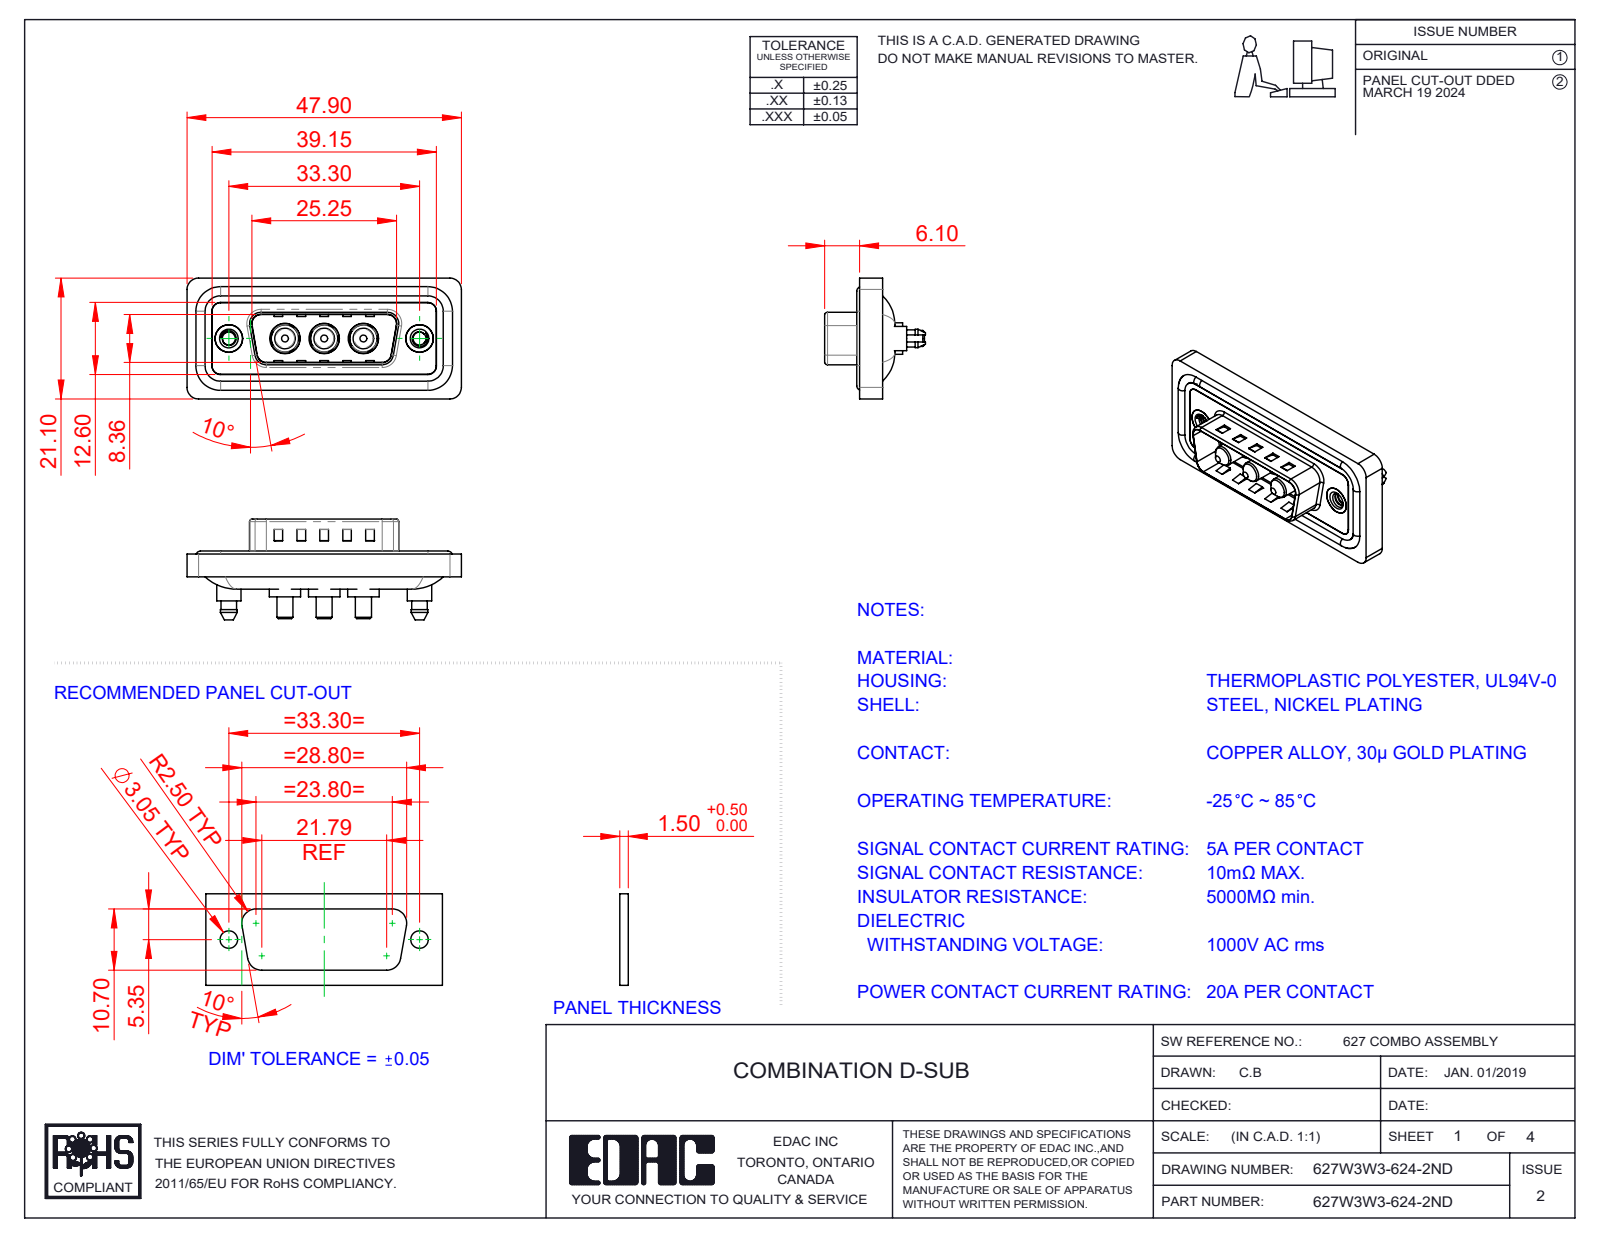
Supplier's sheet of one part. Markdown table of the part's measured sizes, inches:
| quantity | value |
| --- | --- |
| part name | 627Combo Waterproof Housing_15 Contacts; 627Combo Threaded Boardlock_5; 627Combo Housing_3W3; 627Combo Shell Front_15 Contacts (+4 more) |
| STEP written by | SolidWorks 2023 (CONFIG_CONTROL_DESIGN) |
| units | inches |
| bodies | 13 solids, 622 faces (223 planar, 281 cylindrical, 118 other) |
| overall size | 1.886 × 0.831 × 0.693 |
| volume | 0.349 in³ |
| surface area | 14.09 in² |
| round holes (diameter × count) | 0.191 × 3, 0.209 × 3, 0.089 × 2, 0.157 × 2, 0.189 × 2, 0.197 × 2 |
| round bosses / shafts (diameter × count) | 0.063 × 4, 0.217 × 3, 0.205 × 3, 0.187 × 3, 0.148 × 3, 0.142 × 3, 0.11 × 3, 0.213 × 2 |
| partial cylindrical surfaces (radius × count) | 0.059 × 28, 0.079 × 20, 0.063 × 10, 0.02 × 8, 0.01 × 4, 0.024 × 4, 0.026 × 4, 0.035 × 4 |
| main face-to-face distances | 0.016, 0.043, 0.059, 0.122, 0.063, 0.02, 0.114, 0.157, 0.028, 0.032 |
| hole center spacings | 0.27, 0.386, 0.656, 0.925, 0.539, 1.311 |
